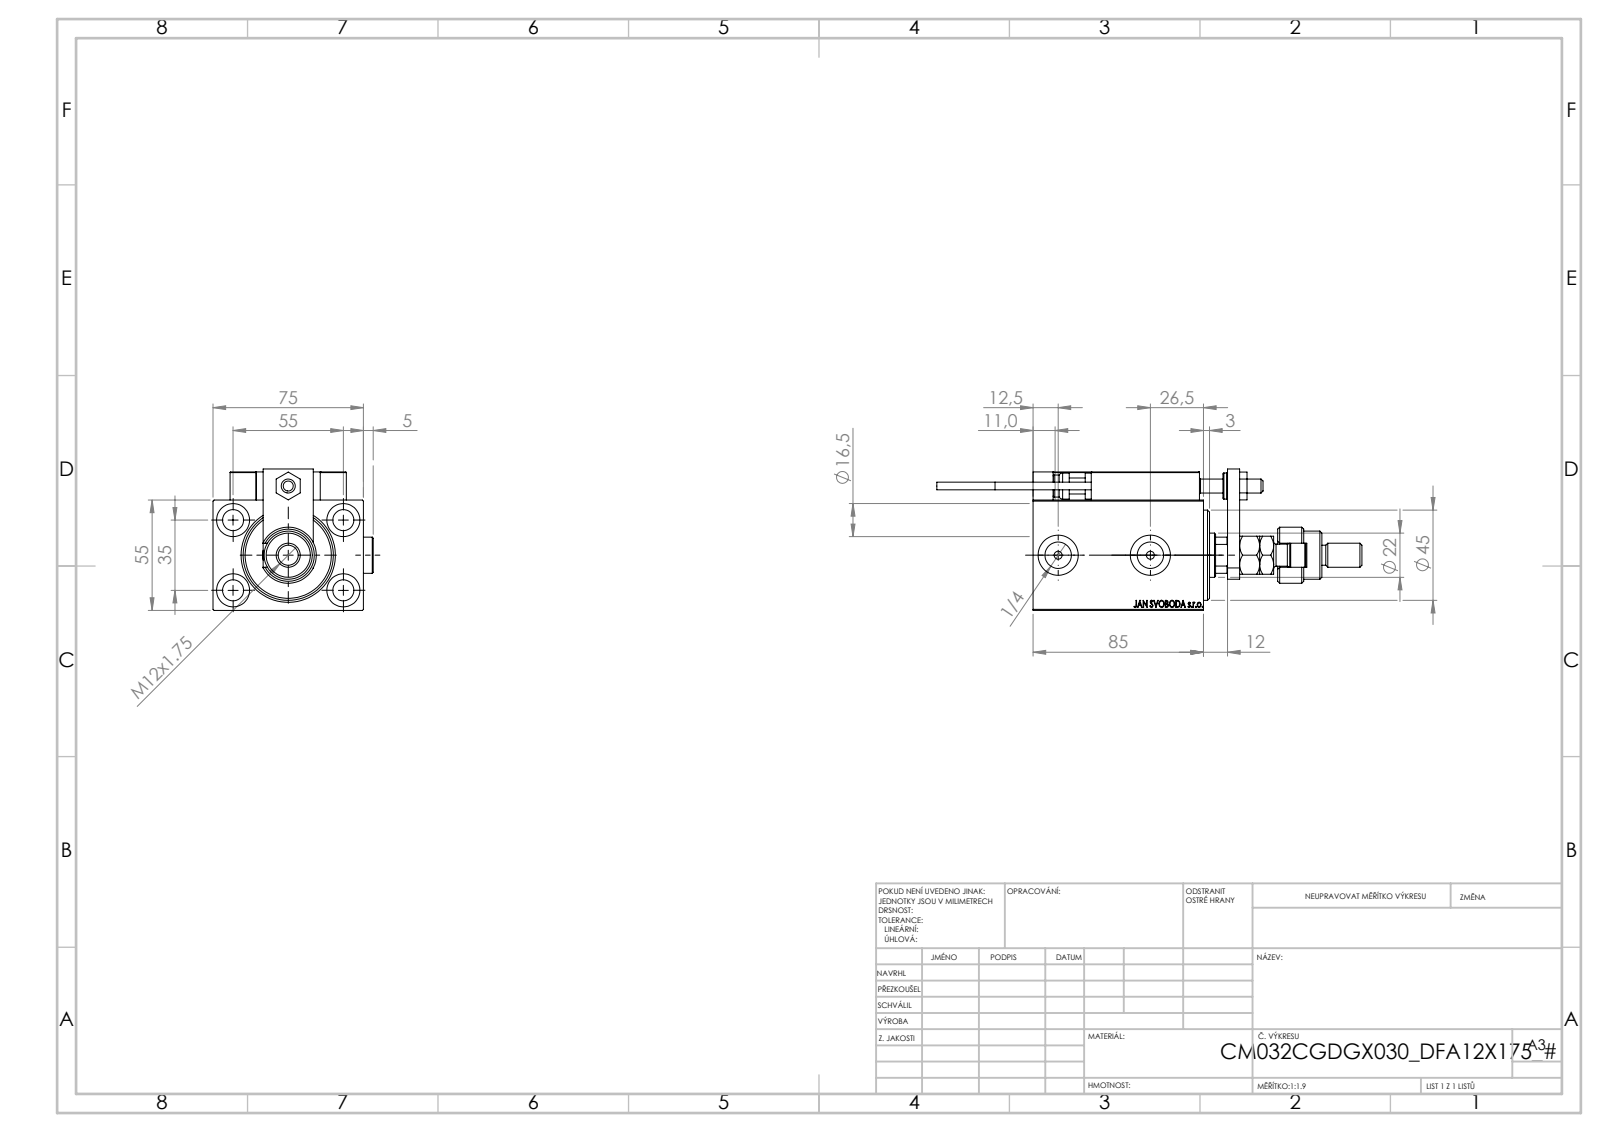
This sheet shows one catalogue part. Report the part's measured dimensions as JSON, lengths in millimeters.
{"part_name": "V450CM_VC_B; SWITCH X; MFA; ALLEN BOLT D8 (+7 more)", "step_written_by": "SolidWorks 2019 (CONFIG_CONTROL_DESIGN)", "units": "millimeters", "bodies": {"solids": 27, "faces": 1421, "planar": 622, "cylindrical": 217, "other": 582}, "overall_size": [212, 79.9, 70.5], "volume_mm3": 363619, "surface_area_mm2": 100397, "round_holes": [[4, 6], [8, 5], [10.5, 5], [16.5, 5], [3.2, 4], [5, 2], [13.16, 2], [20, 2], [7, 1], [22, 1], [25.5, 1], [32, 1]], "round_bosses_or_shafts": [[18, 3], [11, 2], [5, 2], [3.8, 2], [28, 1], [24, 1], [13, 1], [12, 1]], "partial_cylinders_radius": [[0.3, 30], [3, 2], [9.75, 1], [10.5, 1]], "face_to_face_distances": [55, 75, 14, 12, 10, 69, 18, 25, 5, 6], "hole_center_spacings": [32.6, 11.37, 20, 29.59, 29.69, 32.33, 35, 36.06]}
